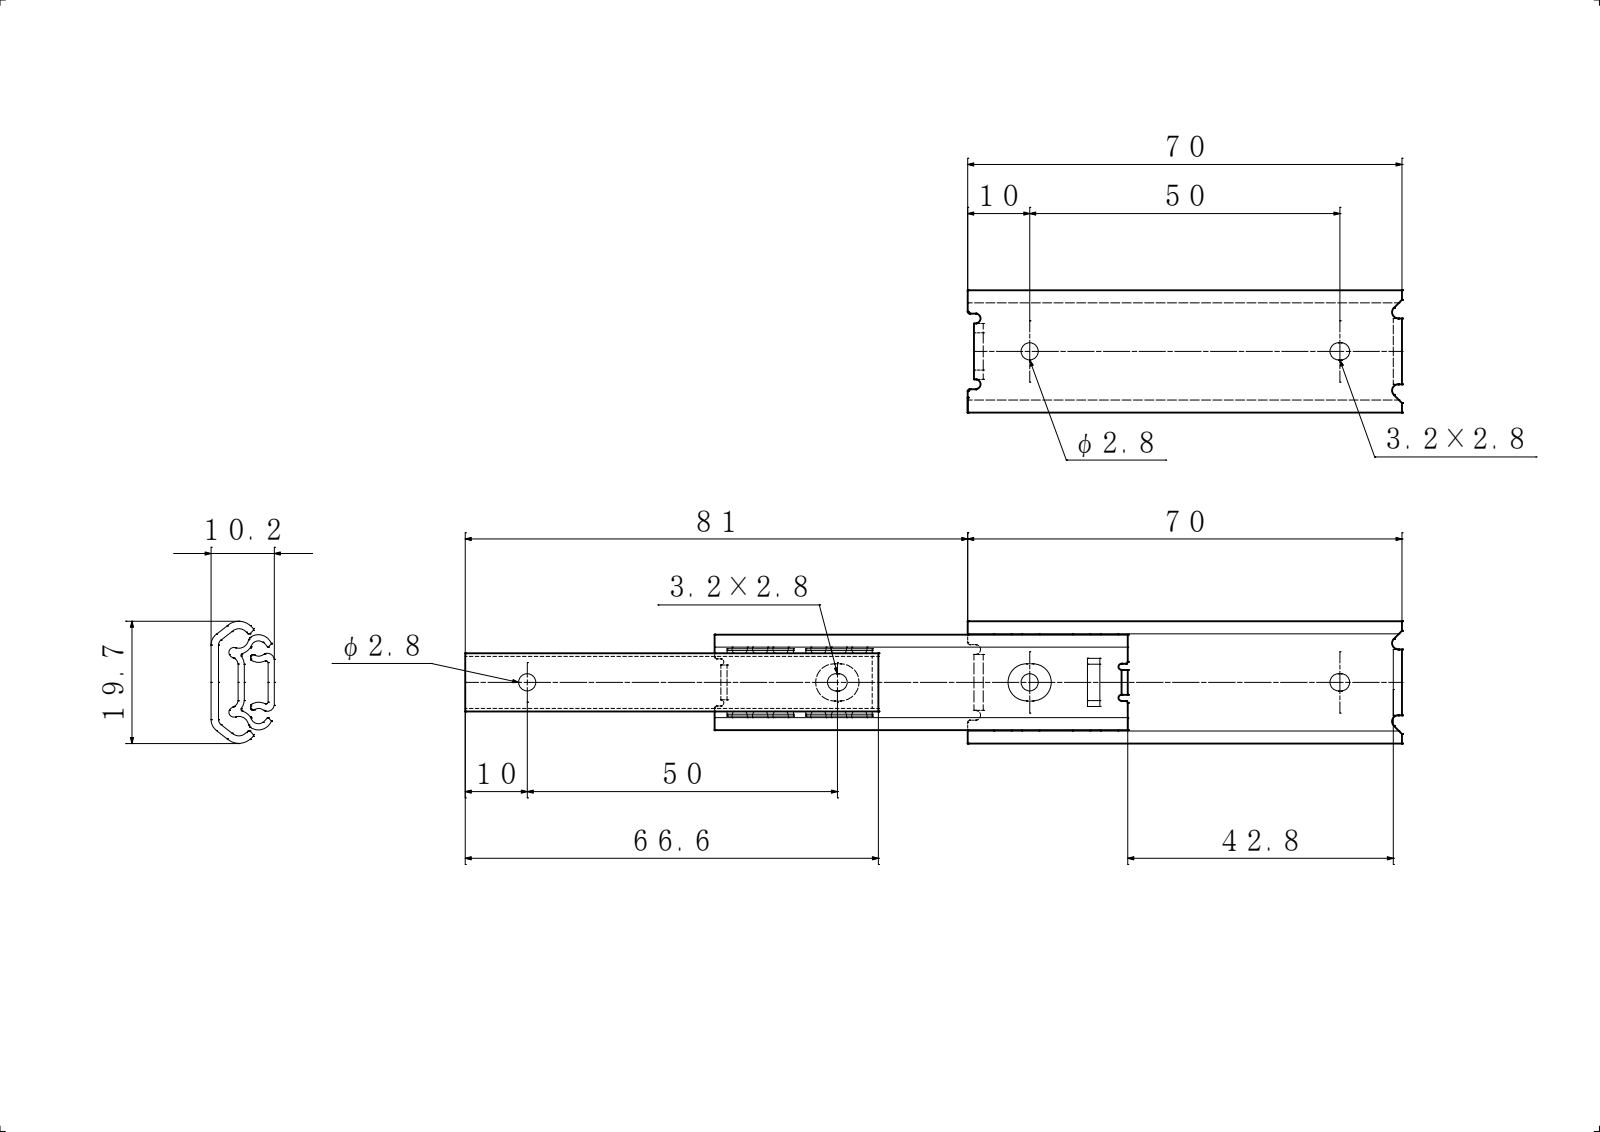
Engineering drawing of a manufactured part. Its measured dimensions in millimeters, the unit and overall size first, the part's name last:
Units: millimetres
Overall size (bounding box): 150.8 × 19.7 × 10.2
Round holes (diameter × count): ⌀2.8 ×2
Partial cylindrical surfaces — rounded edges, fillets, slot ends (radius × count): R0.5 ×22, R1 ×20, R0.3 ×9, R0.1 ×4, R0.8 ×4, R1.4 ×4, R3 ×4, R0.1 ×2
Main face-to-face distances: 1.2, 1, 4.84, 9, 10.2, 9.2, 8, 4.36, 3.16, 5.84
Hole centre spacings: 80.8
Volume: 4 977 mm³ · Surface area: 10 033 mm²
Bodies: 3 solids, 230 faces (108 planar, 122 cylindrical, 0 other)
Part name (STEP PRODUCT): UC200T-70 IM; UC200T-70 CM; UC200T-70 OM; UC200T-70
STEP written by: SolidWorks 2019 (CONFIG_CONTROL_DESIGN)
